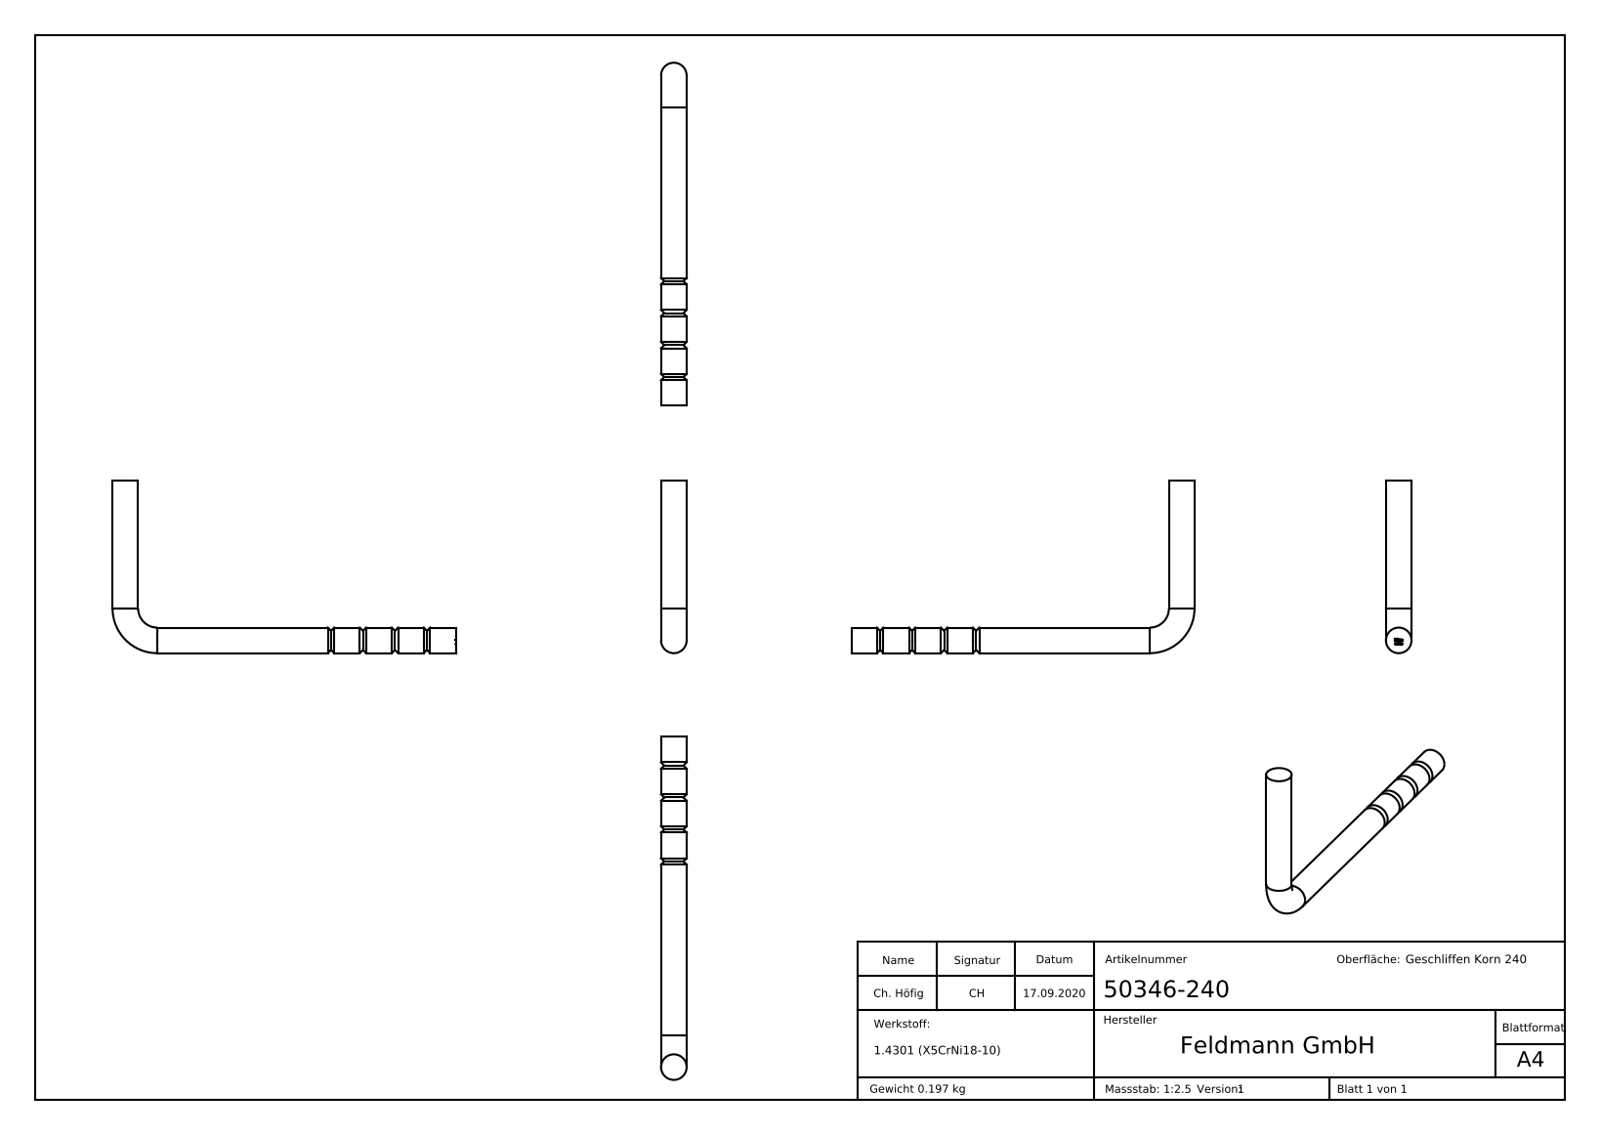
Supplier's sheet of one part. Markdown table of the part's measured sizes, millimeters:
| quantity | value |
| --- | --- |
| part name | 50346-240 |
| STEP written by | SolidWorks 2018 (CONFIG_CONTROL_DESIGN) |
| units | millimeters |
| bodies | 1 solid, 261 faces (131 planar, 14 cylindrical, 116 other) |
| overall size | 161 × 81 × 12 |
| volume | 24 472 mm³ |
| surface area | 9 067 mm² |
| round holes (diameter × count) | 5 × 1 |
| round bosses / shafts (diameter × count) | 12 × 2 |
| main face-to-face distances | 1.19, 1.46, 1.35, 0.53, 1.88, 1.47, 1.64, 1.2, 2.12, 0.66 |
